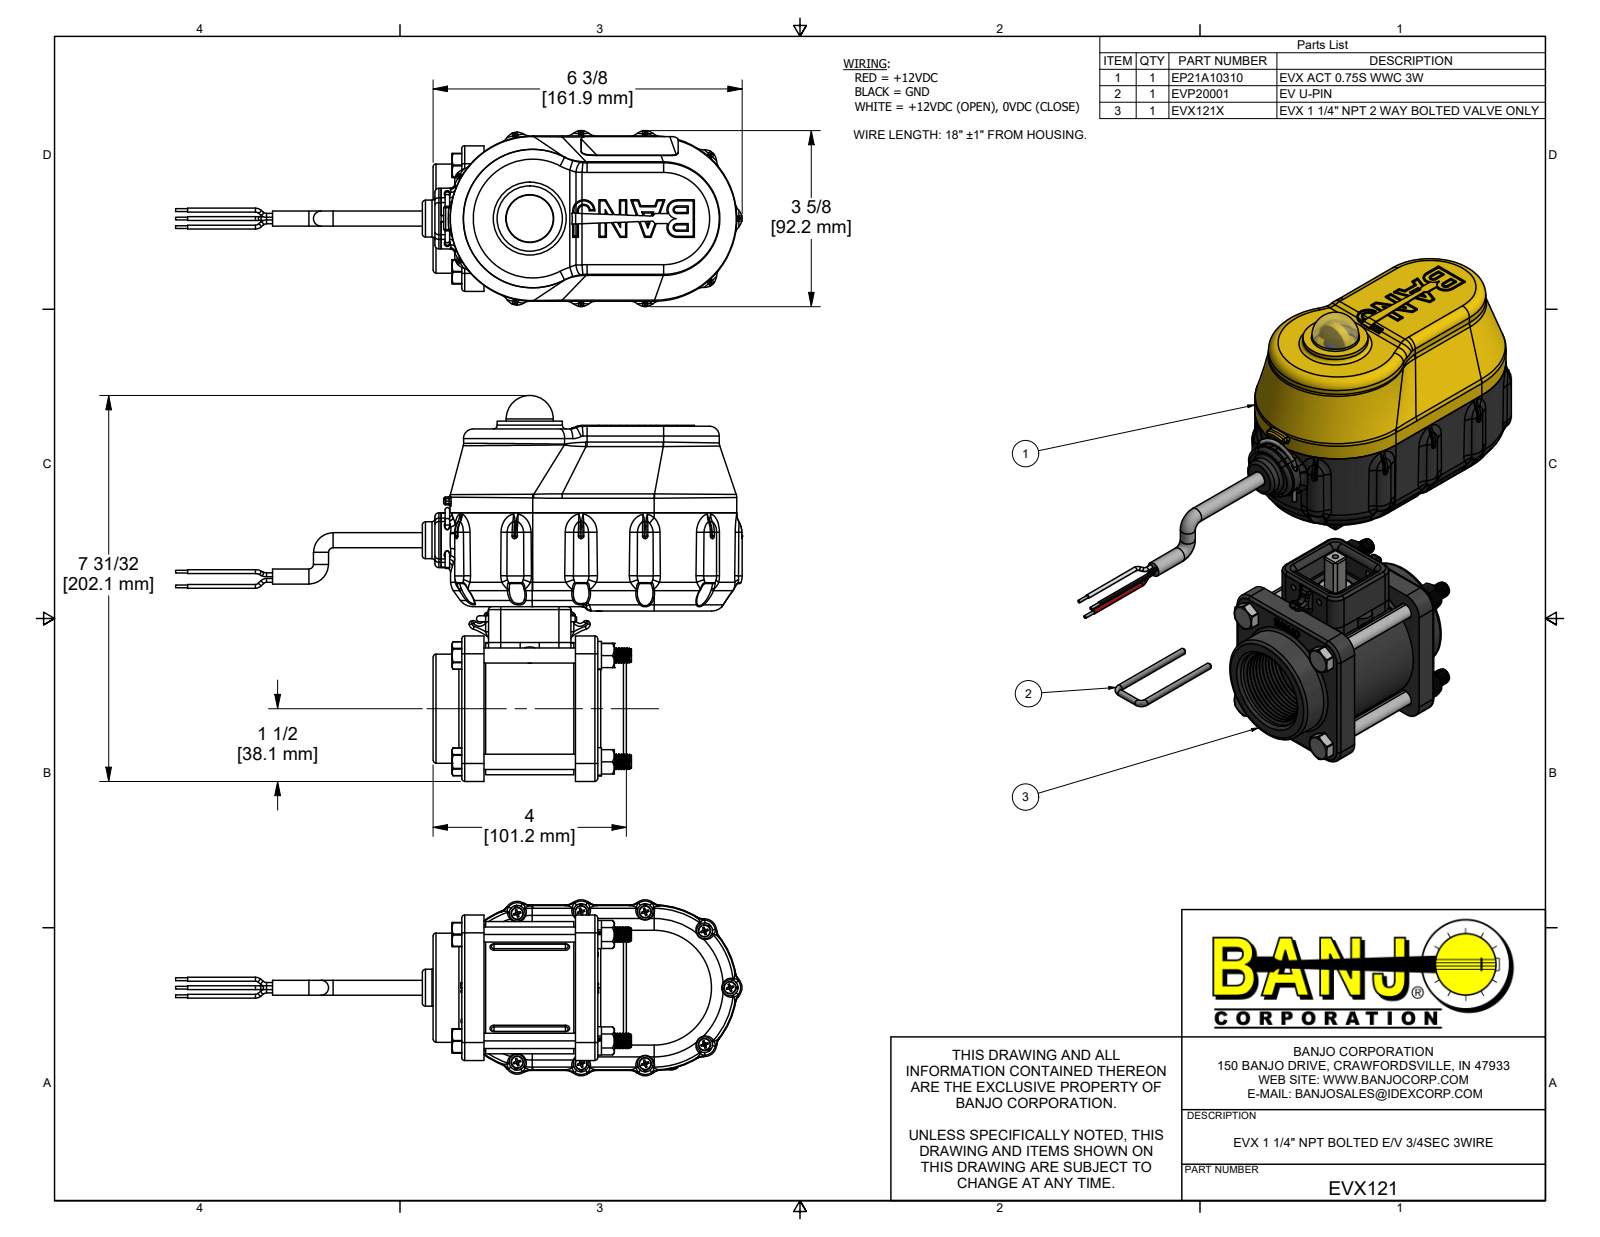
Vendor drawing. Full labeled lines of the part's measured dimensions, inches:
Part name (STEP PRODUCT): EVX121; EVX121X; MEVX10254A; MEVX10254AX (+8 more)
STEP written by: Autodesk Inventor 2019 (AUTOMOTIVE_DESIGN)
Units: inches
Bodies: 96 solids, 11611 faces (2962 planar, 3465 cylindrical, 5184 other)
Overall size (bounding box): 49.551 × 7.957 × 3.63
Volume: 48.71 in³ · Surface area: 859.6 in²
Round holes (diameter × count): ⌀0.095 ×11, ⌀0.15 ×11, ⌀0.08 ×7, ⌀0.107 ×4, ⌀0.126 ×4, ⌀0.135 ×4, ⌀0.136 ×4, ⌀0.148 ×4, ⌀0.15 ×4, ⌀0.17 ×4, ⌀0.252 ×4, ⌀0.322 ×4
Round bosses / shafts (diameter × count): ⌀0.268 ×60, ⌀0.25 ×17, ⌀0.08 ×15, ⌀0.14 ×11, ⌀0.108 ×11, ⌀0.085 ×11, ⌀0.058 ×6, ⌀0.313 ×5
Partial cylindrical surfaces — rounded edges, fillets, slot ends (radius × count): R0.013 ×180, R0.04 ×145, R0.01 ×84, R0.02 ×72, R0.06 ×58, R0.005 ×53, R0.03 ×38, R0.08 ×28
Main face-to-face distances: 0.1, 2.565, 0.211, 0.06, 0.151, 0.46, 2.345, 0.055, 0.125, 1.896
Hole centre spacings: 1.046, 1.55, 1.662, 1.891, 2.192, 2.656, 2.69, 2.715
